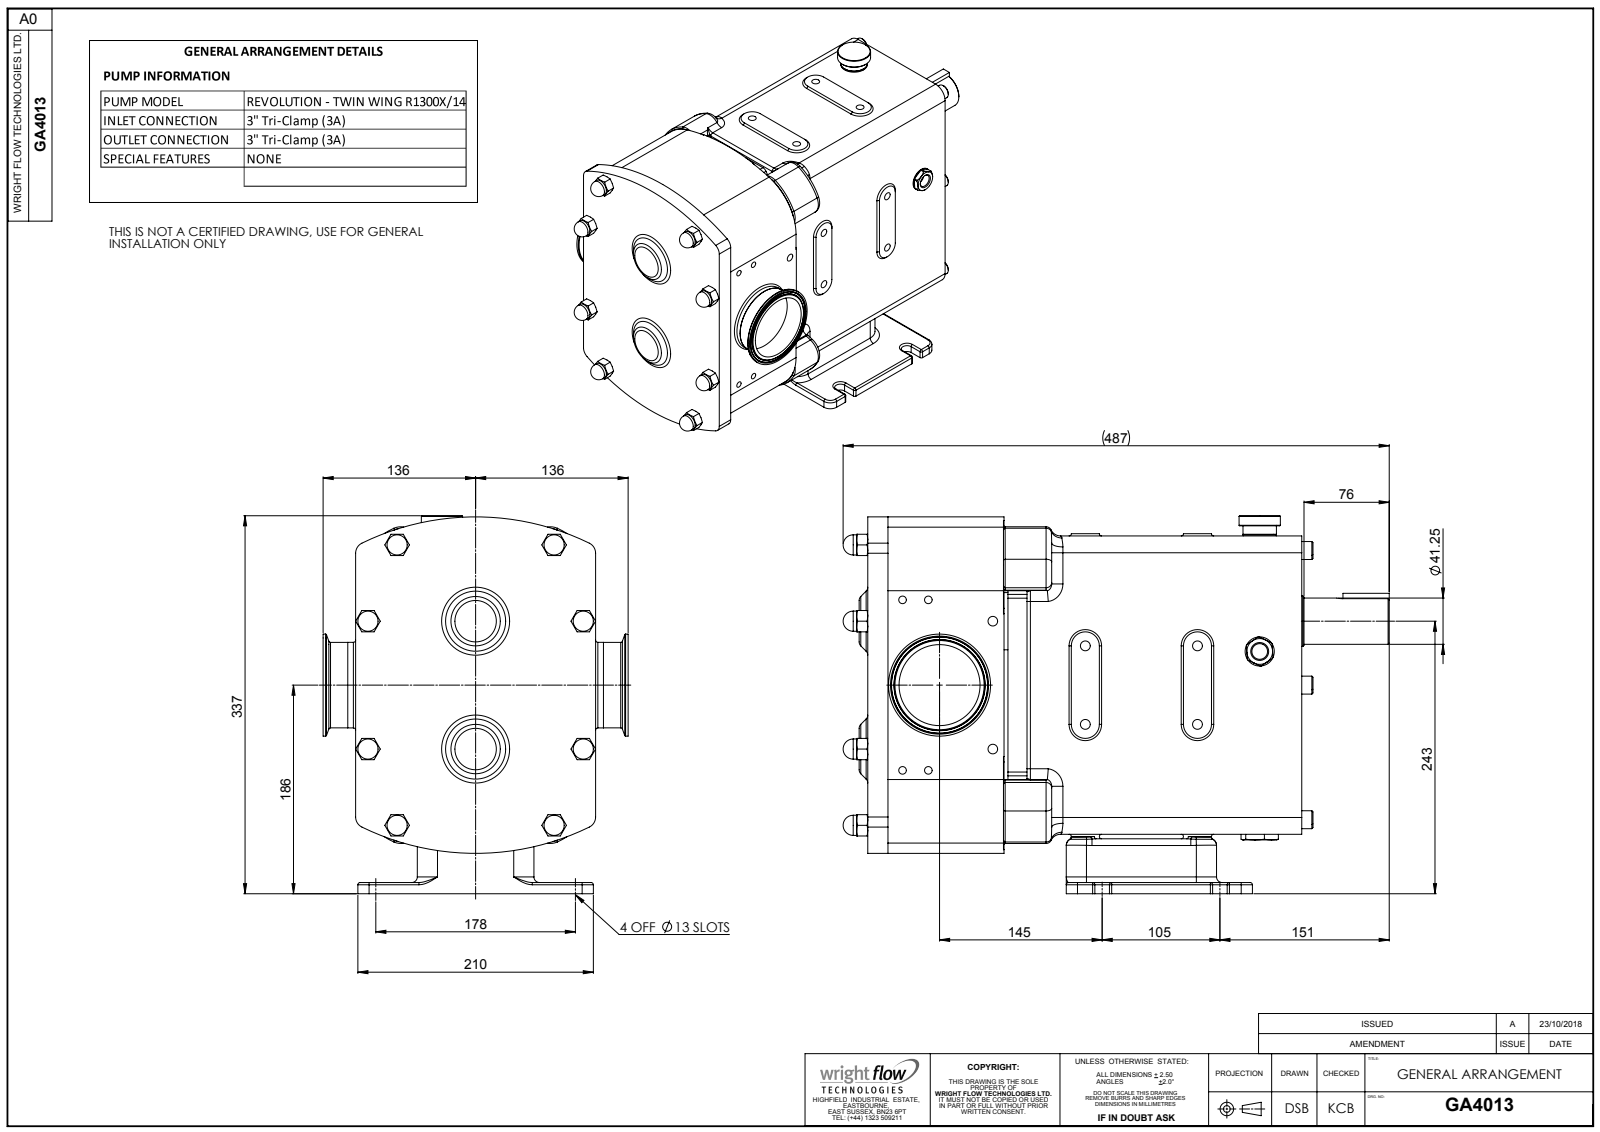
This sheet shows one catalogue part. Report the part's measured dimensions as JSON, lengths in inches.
{"part_name": "GA4013; Copy of RA94-5121-55M^GA4013; Copy of R1300 CPP H TSD^GA4013", "step_written_by": "SolidWorks 2023 (AUTOMOTIVE_DESIGN)", "units": "inches", "bodies": {"solids": 3, "faces": 956, "planar": 299, "cylindrical": 284, "other": 373}, "overall_size": [19.173, 13.268, 10.709], "volume_in3": 1139, "surface_area_in2": 1103, "round_holes": [[0.346, 8], [0.268, 4], [0.339, 2], [0.551, 1], [1.331, 1], [2.844, 1]], "round_bosses_or_shafts": [[0.709, 8], [0.63, 6], [3.583, 1], [3.004, 1], [3, 1], [2.008, 1], [1.772, 1], [1.624, 1]], "partial_cylinders_radius": [[0.079, 38], [0.394, 30], [0.197, 19], [0.232, 8], [0.591, 8], [0.709, 8], [0.118, 4], [0.236, 4]], "face_to_face_distances": [5.984, 4.783, 10.453, 15.236, 1.22, 7.205, 4.921, 0.138, 10.315, 1.693], "hole_center_spacings": [2.756, 3.937, 4.806, 0.906, 2.194, 2.384, 2.921, 3.018]}
